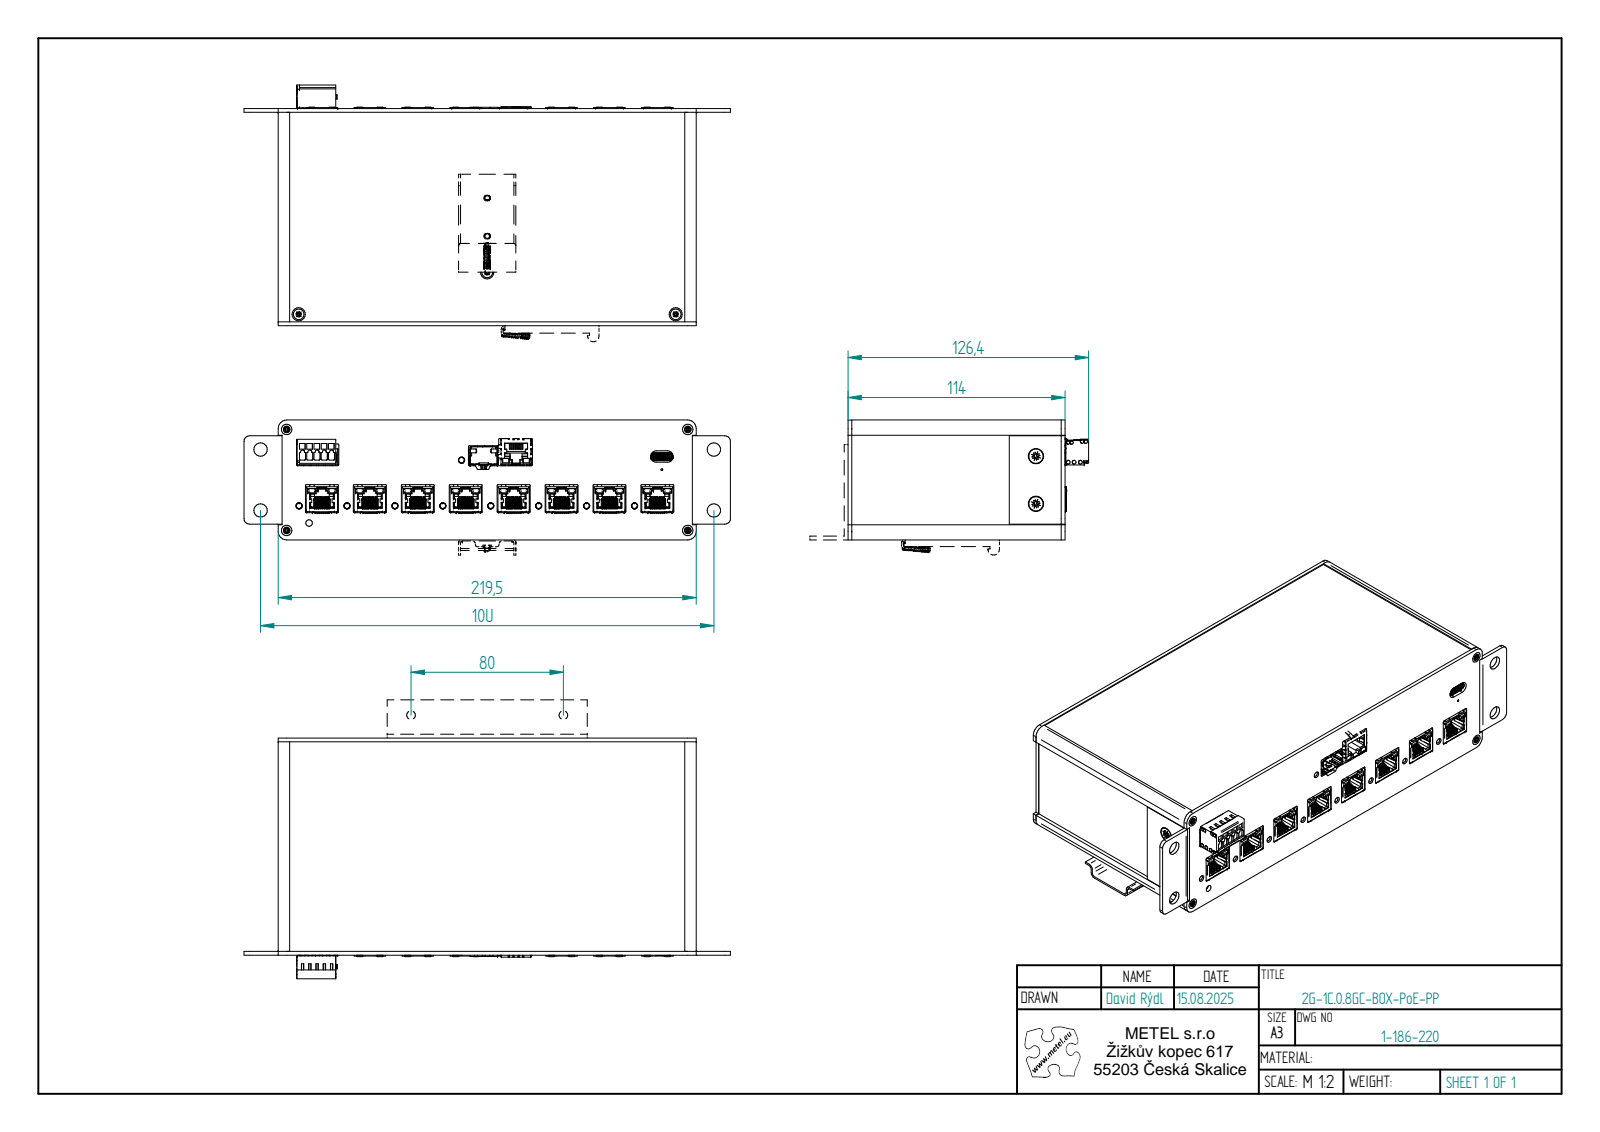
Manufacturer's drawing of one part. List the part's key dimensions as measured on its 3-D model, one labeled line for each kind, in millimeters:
Part name (STEP PRODUCT): 2G-1C.0.8.GC; Profil 210-2C.0.8-zak; 1-186-220-2G-1C.0.8.GC-Predni; 734-205 (+8 more)
STEP written by: Solid Edge (AUTOMOTIVE_DESIGN)
Units: millimetres
Bodies: 69 solids, 14042 faces (9493 planar, 3380 cylindrical, 1169 other)
Overall size (bounding box): 255.5 × 146.35 × 73.41
Volume: 280 676 mm³ · Surface area: 249 659 mm²
Round holes (diameter × count): ⌀1 ×21, ⌀2 ×12, ⌀3.3 ×12, ⌀3.2 ×10, ⌀3.5 ×9, ⌀2.46 ×6, ⌀1.5 ×5, ⌀0.45 ×4, ⌀2.7 ×4, ⌀7 ×4, ⌀0.4 ×2, ⌀0.5 ×2
Round bosses / shafts (diameter × count): ⌀2.9 ×12, ⌀5.5 ×4, ⌀3 ×4, ⌀5.6 ×3, ⌀2.63 ×3, ⌀2 ×3, ⌀7.5 ×2, ⌀4 ×2
Partial cylindrical surfaces — rounded edges, fillets, slot ends (radius × count): R0.1 ×167, R0.2 ×85, R0.5 ×84, R0.3 ×36, R0.25 ×32, R1 ×30, R0.19 ×28, R0.13 ×27
Main face-to-face distances: 2.88, 59.12, 2, 112, 62, 56.24, 4, 114, 110, 211.5
Hole centre spacings: 25.17, 50.34, 75.51, 100.68, 125.86, 2.54, 7.79, 25.18
